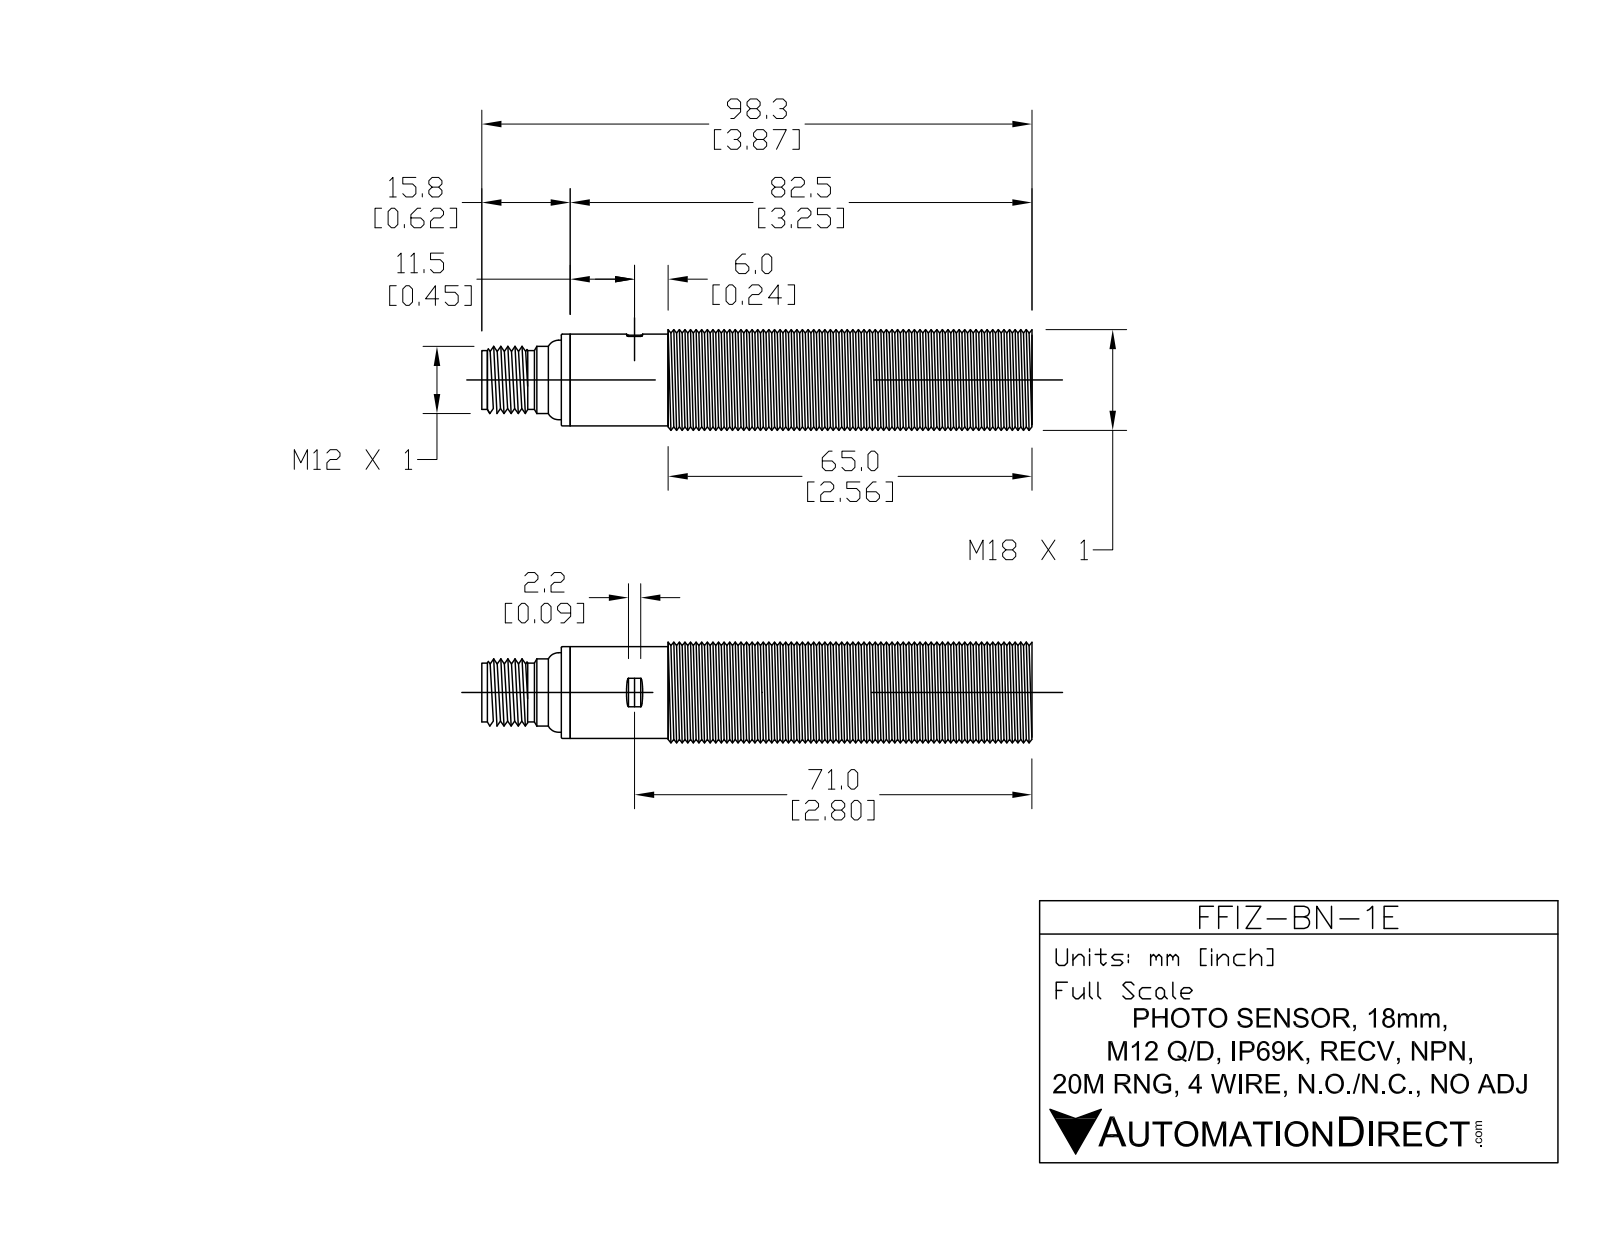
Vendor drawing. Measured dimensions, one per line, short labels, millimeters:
name: FFIZ-BN-1E
written by: SolidWorks 2017 (AUTOMOTIVE_DESIGN)
unit: mm
bodies: 5 solids, 118 faces (21 planar, 48 cylindrical, 49 other)
size: 83 × 18 × 18
volume: 17 710 mm³; area: 6 755 mm²
holes: 1× ⌀7.1, 1× ⌀8.3, 1× ⌀12.7, 1× ⌀14.8, 1× ⌀15.5
bosses: 4× ⌀1, 1× ⌀18, 1× ⌀16.4, 1× ⌀15.5, 1× ⌀15.3, 1× ⌀14.2, 1× ⌀12.5, 1× ⌀12
rounds: 1× R0.6, 1× R16
face distances: 64.5, 3, 67.5, 0.6, 2.4, 66.9, 69, 68.4, 66, 1.5
